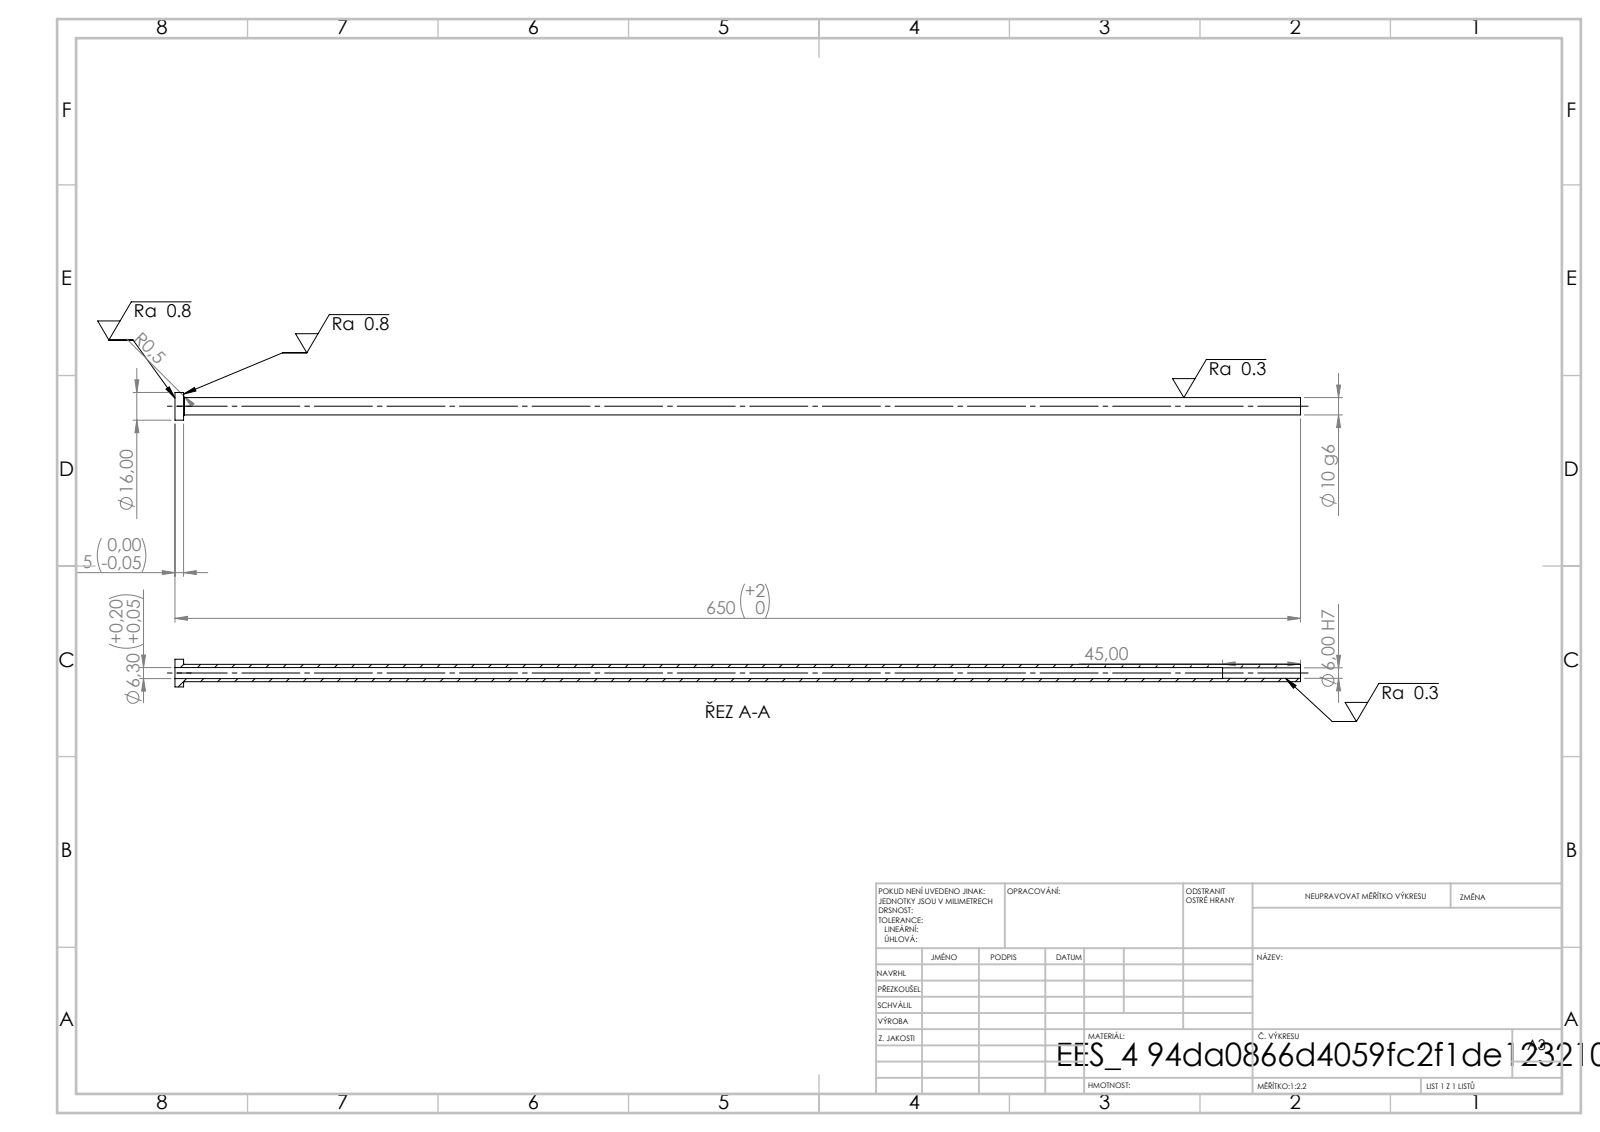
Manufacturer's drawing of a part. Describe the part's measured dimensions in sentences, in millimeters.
Its 3-D file was written by "SolidWorks 2019 (CONFIG_CONTROL_DESIGN)". It is 1 solid with 14 faces: 4 planar, 8 cylindrical and 2 other. Overall it measures 650 by 16 by 16 millimeters. Its volume is 31 534 cubic millimeters and its surface area 33 676 square millimeters. Round holes: 1 of diameter 6, 1 of diameter 6.3. Round bosses or shafts: 1 of diameter 16, 1 of diameter 10. The main face-to-face distances are 5, 650, 645, 605, 600, 45.
